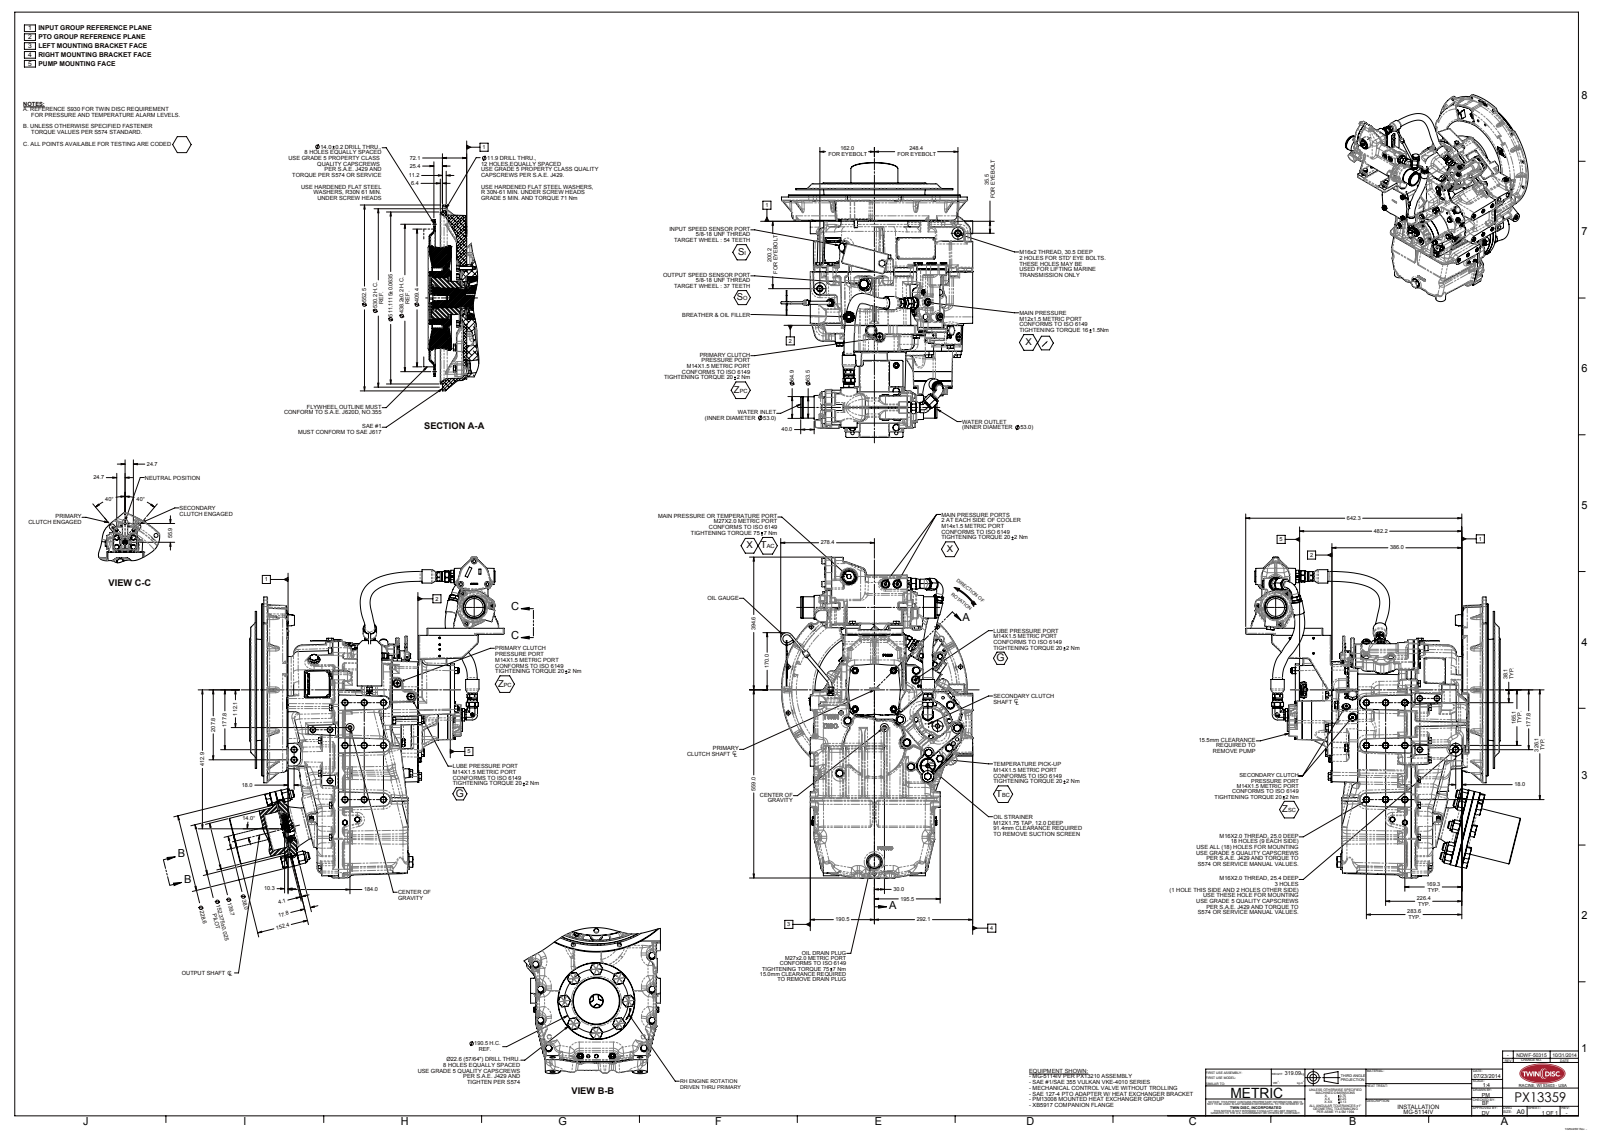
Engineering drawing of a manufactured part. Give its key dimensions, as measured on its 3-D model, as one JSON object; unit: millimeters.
{"part_name": "PX13359", "step_written_by": "SolidWorks 2010 (AUTOMOTIVE_DESIGN)", "units": "millimeters", "bodies": {"solids": 0, "faces": 8809, "planar": 2218, "cylindrical": 2345, "other": 4246}, "overall_size": [954, 816.9, 570.6], "round_holes": [[10, 13], [11.9, 12], [18.8, 11], [5, 9], [14, 8], [16.8, 8], [10.7, 6], [11, 5], [16.5, 5], [22.6, 5], [25, 5], [6.8, 4]], "round_bosses_or_shafts": [[19.8, 28], [19, 9], [16, 9], [31.6, 8], [22.1, 8], [24, 7], [12, 6], [33, 5]], "partial_cylinders_radius": [[8, 114], [2, 100], [2, 97], [5.1, 69], [1, 67], [4, 54], [2.5, 50], [2.5, 48]], "face_to_face_distances": [309.2, 0.8, 310, 4, 159.8, 159, 150.2, 160.2, 159.4, 0.4], "hole_center_spacings": [95.3, 459.2, 19.1, 137.2, 265.1, 265.1, 374.9, 512.1]}
